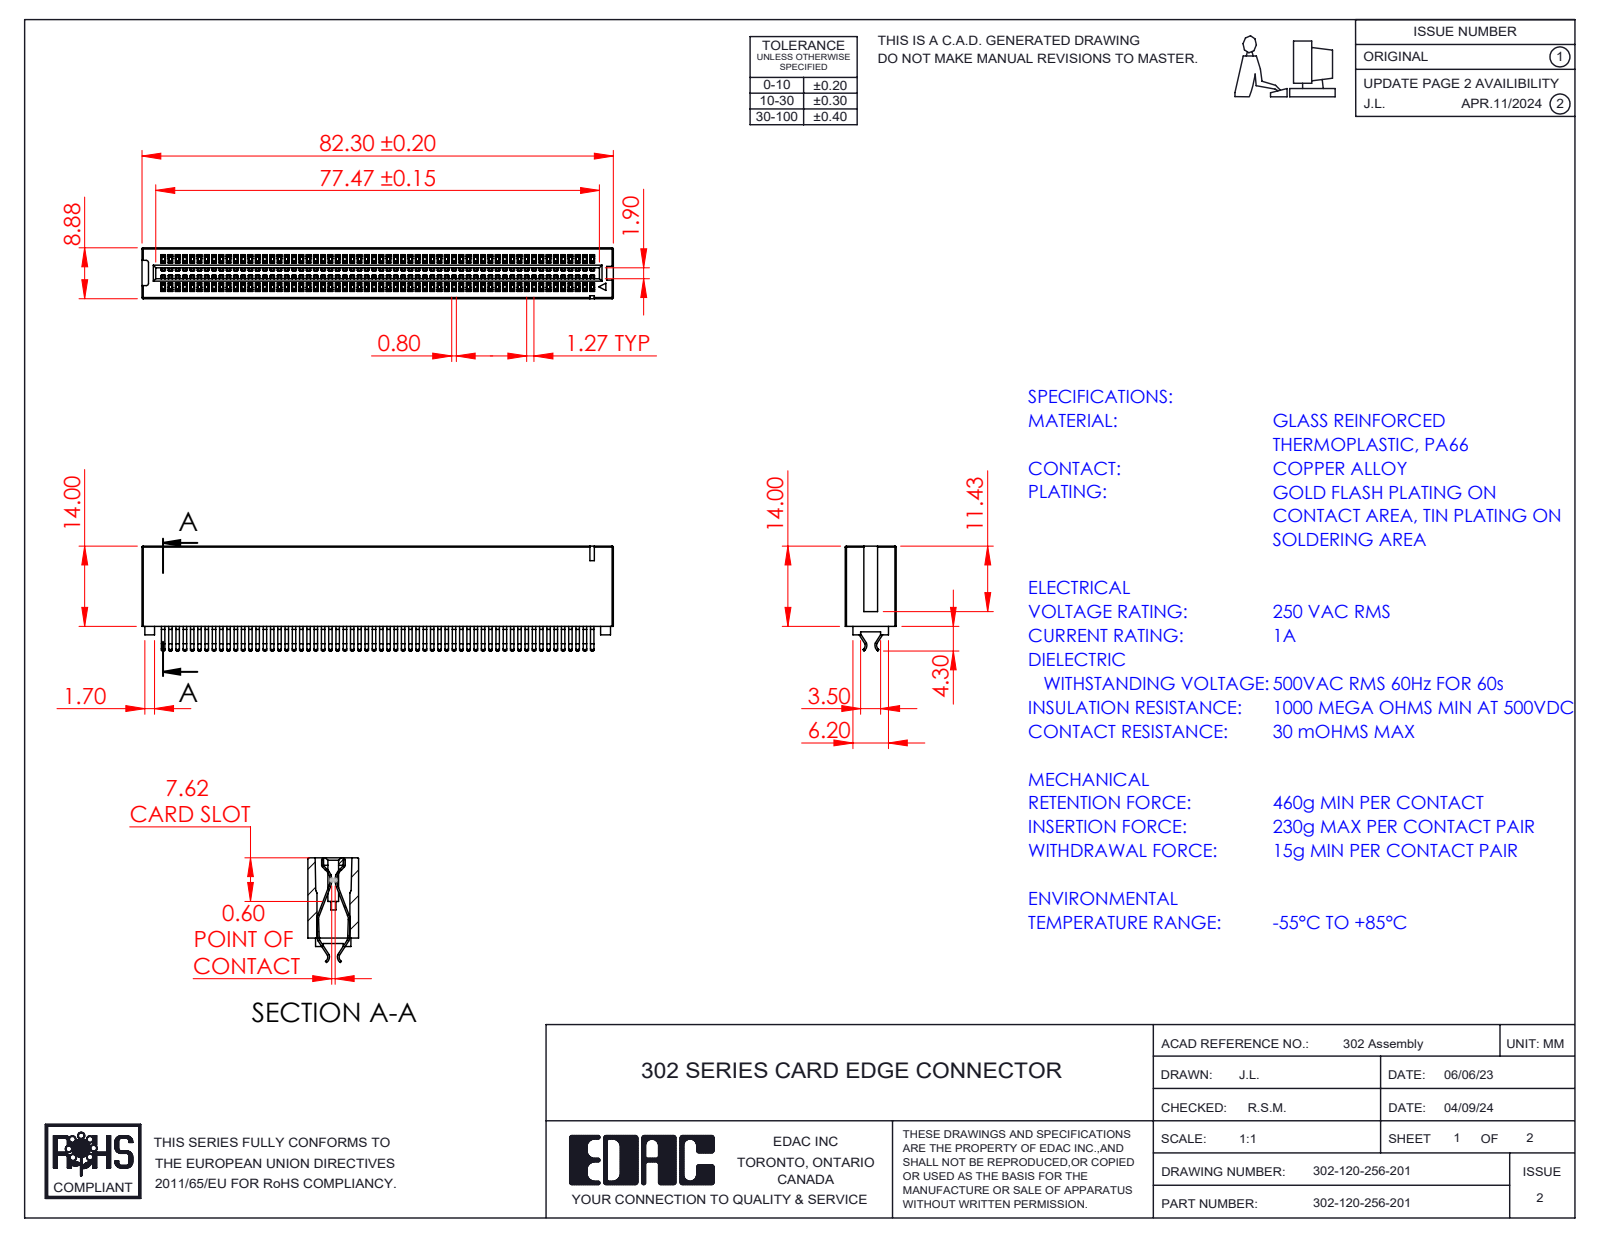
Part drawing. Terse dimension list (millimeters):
name: 302-120-256-201; Contact_302-290-X56; HSG_Vertical HSG
written by: SolidWorks 2023 (CONFIG_CONTROL_DESIGN)
unit: mm
bodies: 121 solids, 5766 faces (3829 planar, 1933 cylindrical, 4 other)
size: 82.3 × 18.3 × 8.88
volume: 6 275 mm³; area: 18 135 mm²
rounds: 368× R0.2, 2× R0.11, 2× R0.4, 2× R0.41, 2× R0.93, 2× R1.05, 2× R1.23, 2× R1.25
face distances: 8.88, 1.27, 2.54, 3.81, 5.08, 7.62, 6.35, 8.89, 10.16, 12.7
